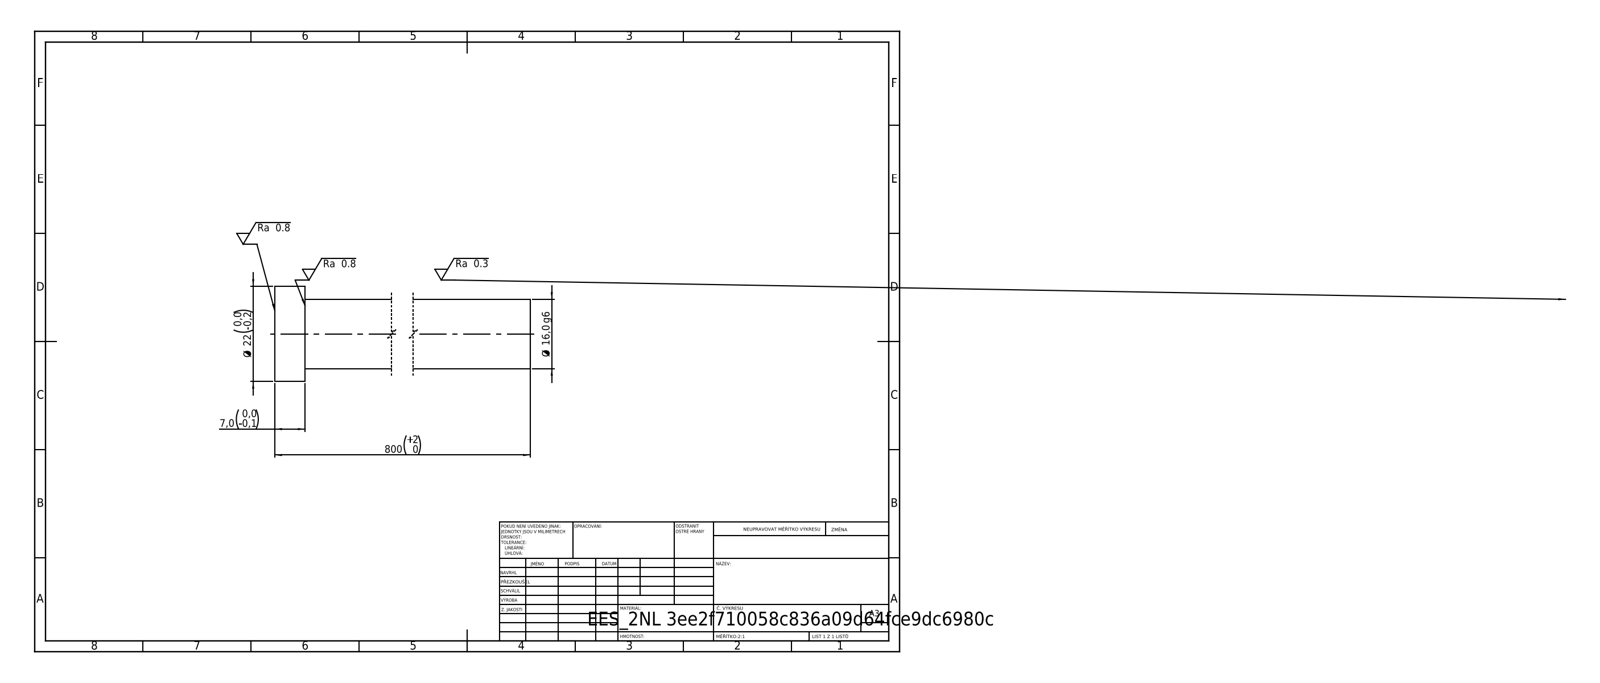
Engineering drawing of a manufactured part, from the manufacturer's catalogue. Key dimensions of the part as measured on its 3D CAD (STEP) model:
STEP written by: SolidWorks 2019 (CONFIG_CONTROL_DESIGN)
Units: millimetres
Bodies: 1 solid, 7 faces (3 planar, 4 cylindrical, 0 other)
Overall size (bounding box): 800 × 22 × 22
Volume: 162 103 mm³ · Surface area: 41 105 mm²
Round bosses / shafts (diameter × count): ⌀22 ×1, ⌀16 ×1
Main face-to-face distances: 800, 7, 793
